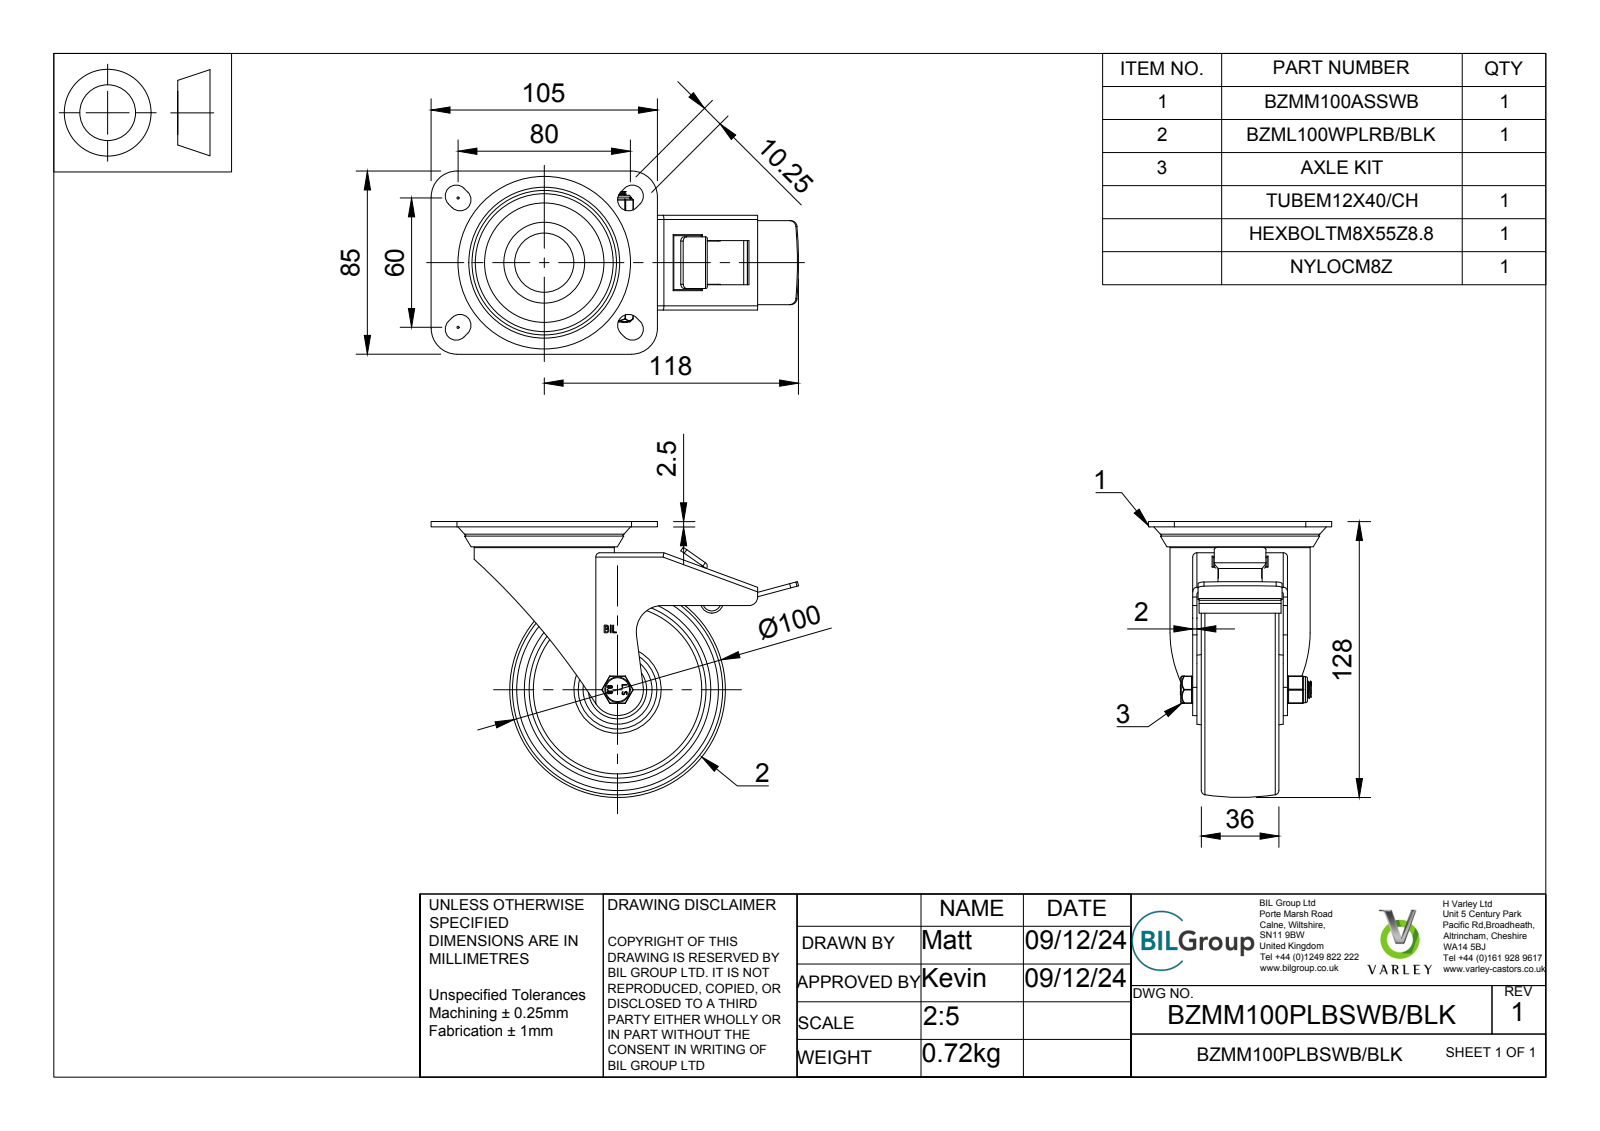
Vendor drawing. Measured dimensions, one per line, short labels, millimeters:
name: BZMM100PLBSWB/BLK v3; BZMM100ASSWB v1; ZINC PLATED, PRESSED STEEL TOP PLATE; ZINC PLATED, PRESSED STEEL TOP PLATE Geometry (+7 more)
written by: Autodesk Translation Framework v13.20.0.188 (AP242_MANAGED_MODEL_BASED_3D_ENGINEERING_MIM_LF)
unit: mm
bodies: 43 solids, 618 faces (331 planar, 169 cylindrical, 118 other)
size: 170.5 × 128 × 85
volume: 208 259 mm³; area: 119 668 mm²
holes: 2× ⌀0.66, 1× ⌀8, 1× ⌀8.2, 1× ⌀8.4, 1× ⌀8.6, 1× ⌀12, 1× ⌀19, 1× ⌀27, 1× ⌀27.5, 1× ⌀56, 1× ⌀61
bosses: 8× ⌀3.5, 1× ⌀65, 1× ⌀31.5, 1× ⌀23, 1× ⌀17.5, 1× ⌀12.1, 1× ⌀11.9, 1× ⌀11.5
rounds: 22× R0.5, 12× R0.25, 9× R2, 8× R5.12, 6× R1, 5× R12, 4× R0.33, 4× R0.64
face distances: 2, 17.25, 22.75, 40, 24.75, 19.25, 42, 5.5, 2.5, 1
hole spacings: 3.22, 2.49
